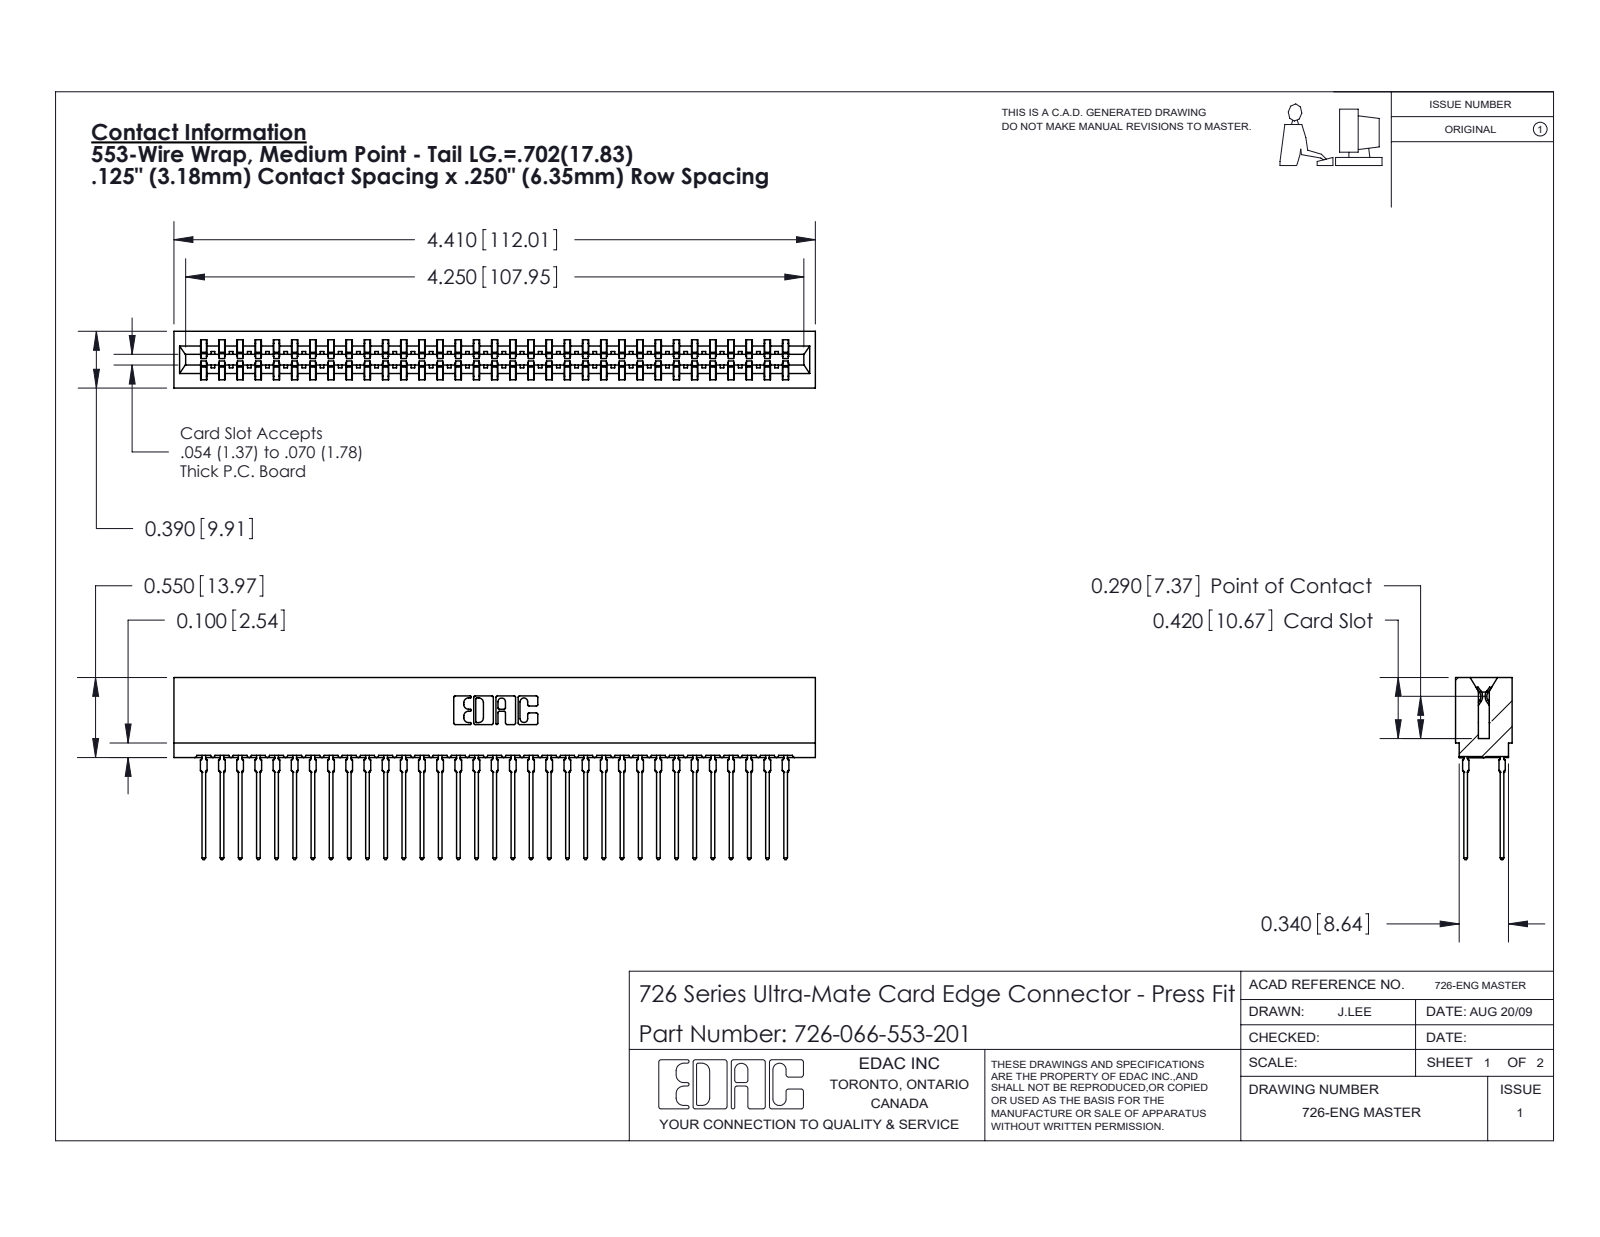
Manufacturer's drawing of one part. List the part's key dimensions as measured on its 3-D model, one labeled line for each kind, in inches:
Part name (STEP PRODUCT): 726 Part_.515 Slot Depth - 01; 746-292-001_553; 726-066-553-201
STEP written by: SolidWorks 2020 (CONFIG_CONTROL_DESIGN)
Units: inches
Bodies: 67 solids, 6004 faces (3091 planar, 1197 cylindrical, 1716 other)
Overall size (bounding box): 4.41 × 1.251 × 0.39
Volume: 0.65 in³ · Surface area: 29.34 in²
Partial cylindrical surfaces — rounded edges, fillets, slot ends (radius × count): R0.021 ×132, R0.015 ×34, R0.01 ×22, R0.005 ×8, R0.011 ×8, R0.007 ×6, R0.031 ×6, R0.026 ×3
Main face-to-face distances: 0.057, 0.333, 0.25, 0.025, 0.307, 0.083, 0.39, 0.275, 0.5, 0.225
